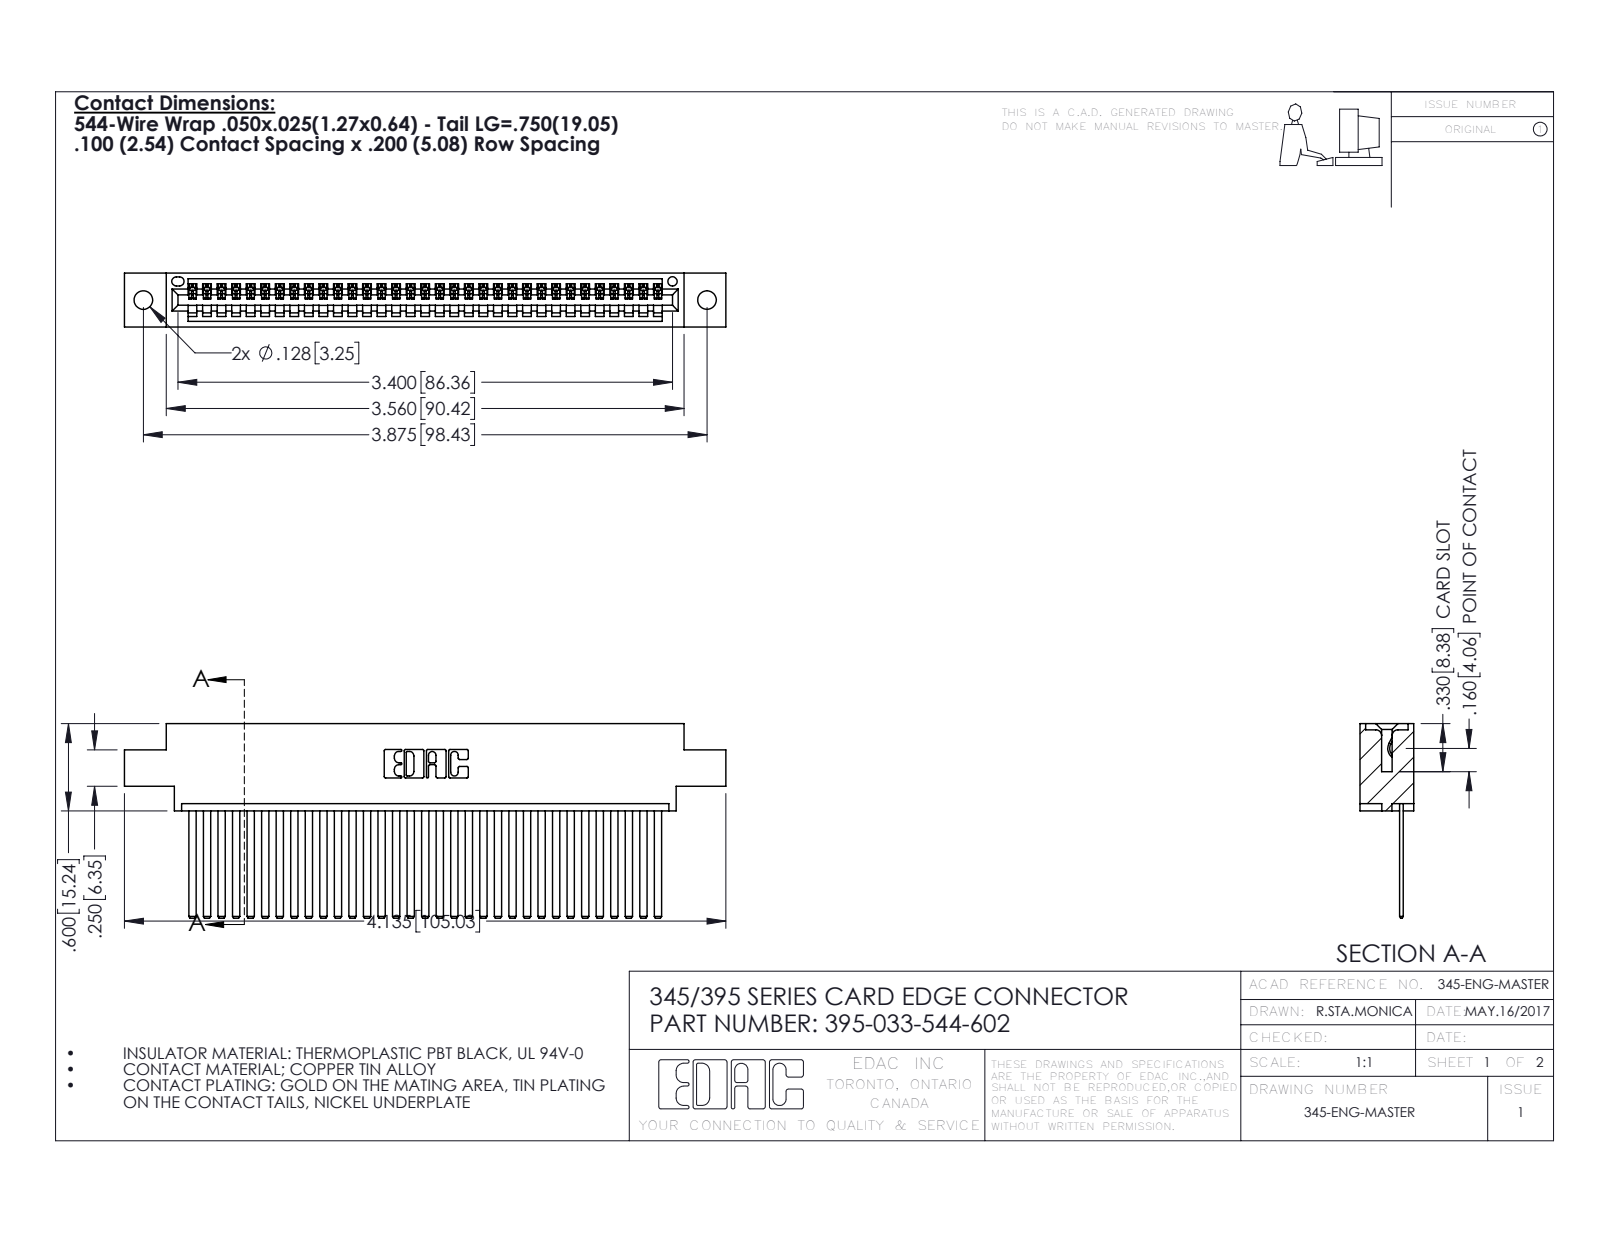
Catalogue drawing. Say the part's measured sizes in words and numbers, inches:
The part is named "345-292-001_345-293-144; 395-033-544-602; 345 Part_0.170 Offset - 0.128 Dia". Its 3-D file was written by "SolidWorks 2016 (CONFIG_CONTROL_DESIGN)". It is 34 solids with 1846 faces: 1272 planar, 574 cylindrical and 0 other. Overall it measures 4.135 by 1.337 by 0.37 inches. Its volume is 0.618 cubic inches and its surface area 22.24 square inches. Round holes: 2 of diameter 0.128, 1 of diameter 0.064. Partial cylindrical surfaces (rounded edges, fillets, slot ends): 66 of radius 0.006, 22 of radius 0.01, 6 of radius 0.007, 6 of radius 0.031, 3 of radius 0.026, 2 of radius 0.031, 2 of radius 0.04, 1 of radius 0.014. The main face-to-face distances are 0.072, 0.298, 0.025, 0.098, 0.272, 0.37, 0.2, 0.225, 0.175, 0.149. The hole center spacings are 0.27, 3.64, 3.875.
